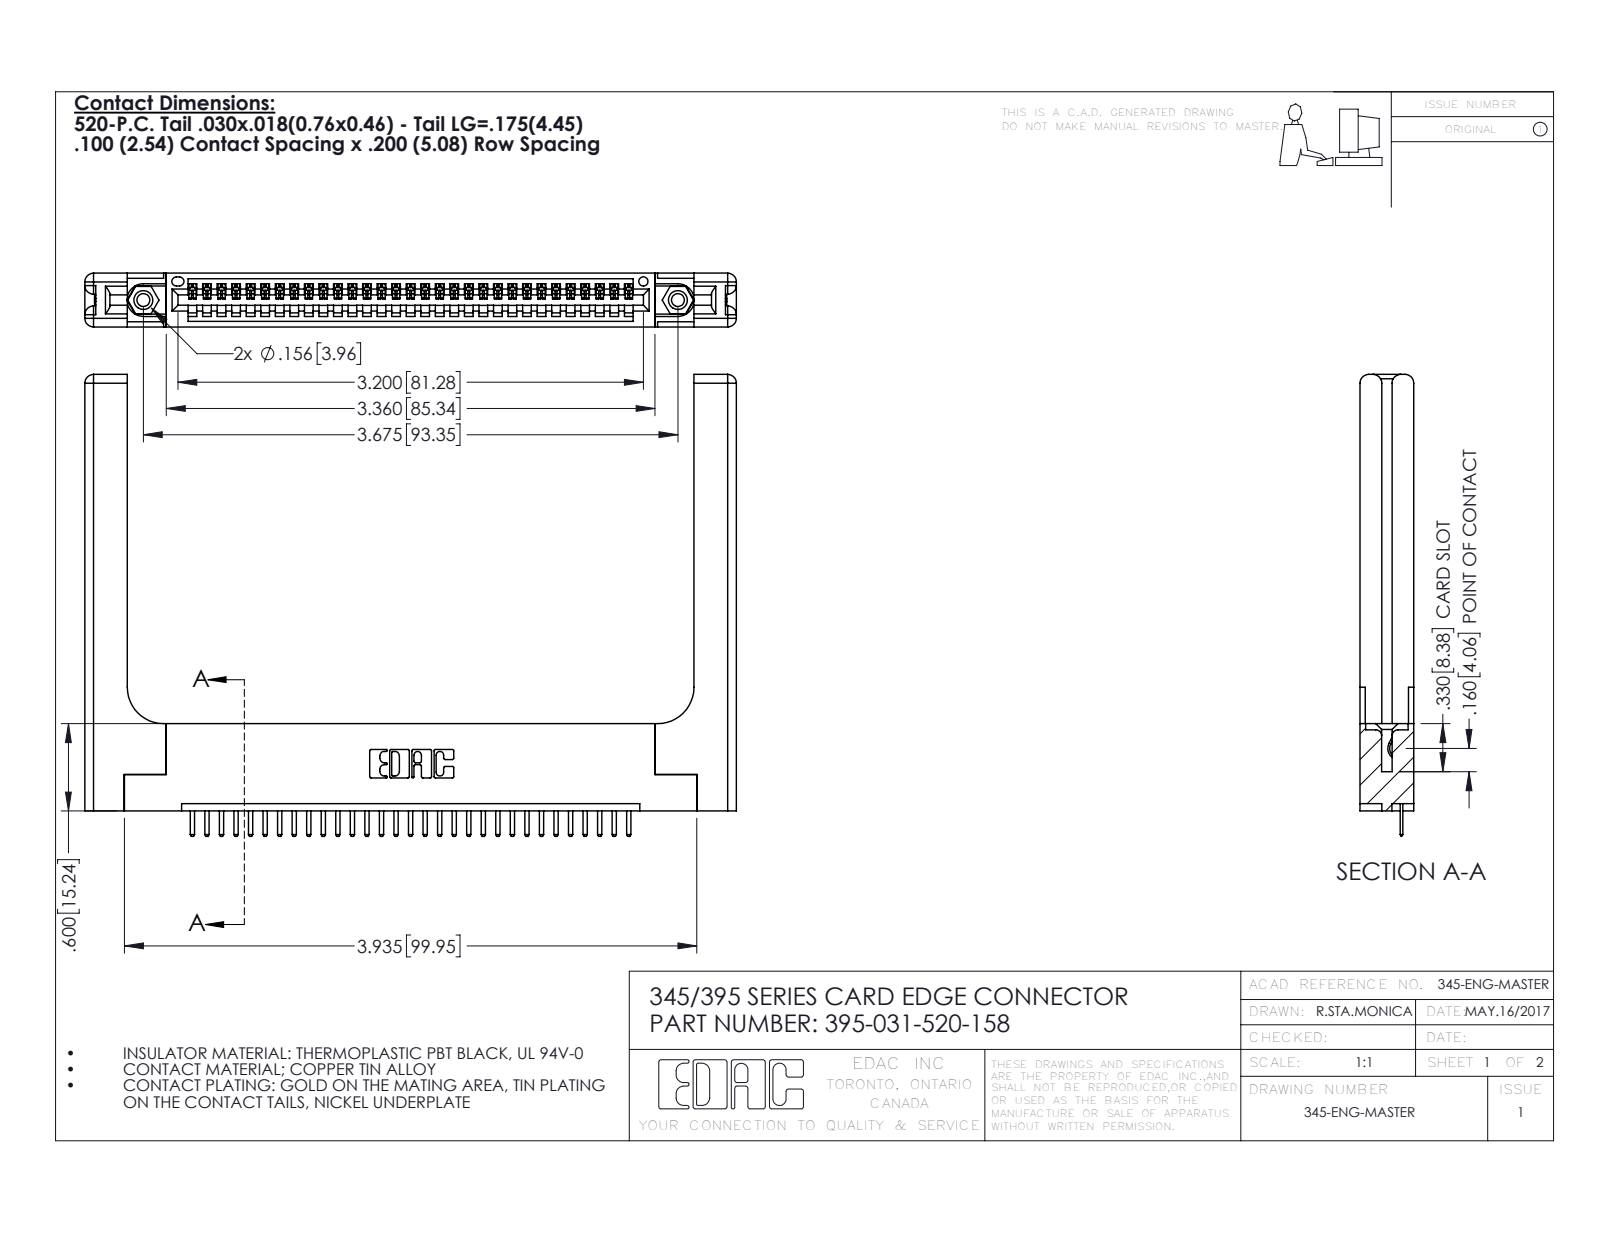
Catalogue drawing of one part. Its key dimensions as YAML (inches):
part_name: "345-292-001_345-293-120; 345-250-001_345-250-001-102; 345 Part_Flush Mounting Lugs - 0.156 Dia-TH; 395-031-520-158 (+1 more)"
step_written_by: "SolidWorks 2016 (CONFIG_CONTROL_DESIGN)"
units: inches
bodies: {solids: 36, faces: 2304, planar: 1530, cylindrical: 714, other: 60}
overall_size: [4.479, 3.175, 0.37]
volume: 1.167
surface_area: 29.43
round_holes:
  - {diameter: 0.089, count: 2}
  - {diameter: 0.125, count: 2}
  - {diameter: 0.156, count: 2}
  - {diameter: 0.064, count: 1}
round_bosses_or_shafts:
  - {diameter: 0.155, count: 2}
partial_cylinders:
  - {radius: 0.01, count: 64}
  - {radius: 0.006, count: 62}
  - {radius: 0.01, count: 22}
  - {radius: 0.06, count: 16}
  - {radius: 0.007, count: 6}
  - {radius: 0.031, count: 6}
  - {radius: 0.026, count: 3}
  - {radius: 0.03, count: 2}
face_to_face_distances: [0.37, 0.072, 0.298, 0.2, 0.148, 0.15, 0.098, 0.272, 0.025, 0.077]
hole_center_spacings: [0.27, 3.44, 3.675]
